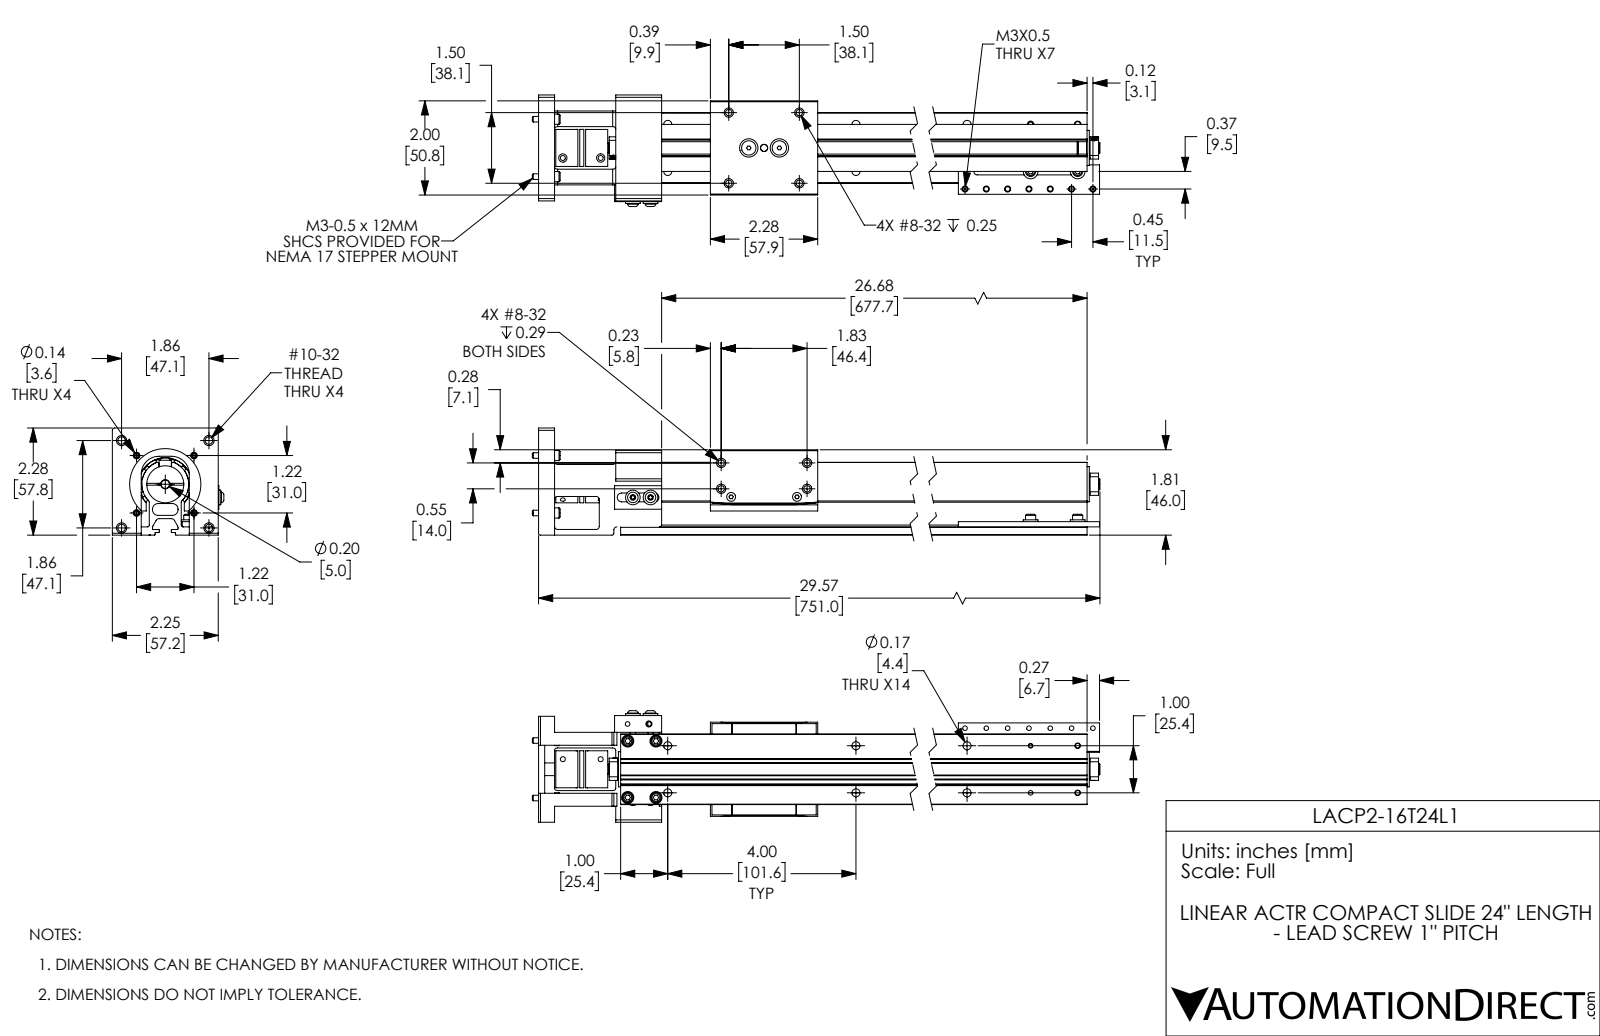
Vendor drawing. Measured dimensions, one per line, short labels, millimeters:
name: LACP2-16T24L1_BODY; LACP2-16T24L1_BLOCK; LACP2-16T24L1
written by: SolidWorks 2017 (AUTOMOTIVE_DESIGN)
unit: mm
bodies: 47 solids, 1257 faces (504 planar, 483 cylindrical, 270 other)
size: 754.4 × 60.2 × 57.8
volume: 464 200 mm³; area: 277 000 mm²
holes: 18× ⌀2.5, 14× ⌀4.4, 10× ⌀3.5, 4× ⌀3.6, 4× ⌀3.7, 4× ⌀4, 4× ⌀6.5, 2× ⌀2.5, 2× ⌀2.7, 2× ⌀3, 2× ⌀3.2, 2× ⌀3.2
bosses: 10× ⌀5.5, 10× ⌀3, 4× ⌀7.9, 4× ⌀3, 2× ⌀7.8, 2× ⌀5.7, 2× ⌀4.2, 2× ⌀3.5
rounds: 17× R0.3, 9× R1.3, 8× R1, 7× R1.7, 4× R0.5, 4× R1.9, 4× R2, 4× R3
face distances: 4.4, 17.2, 4.4, 10.4, 27.7, 10.6, 17, 6.2, 12.6, 6.4
hole spacings: 25.4, 101.6, 104.7, 203.2, 204.8, 30.5, 21.9, 33.3
